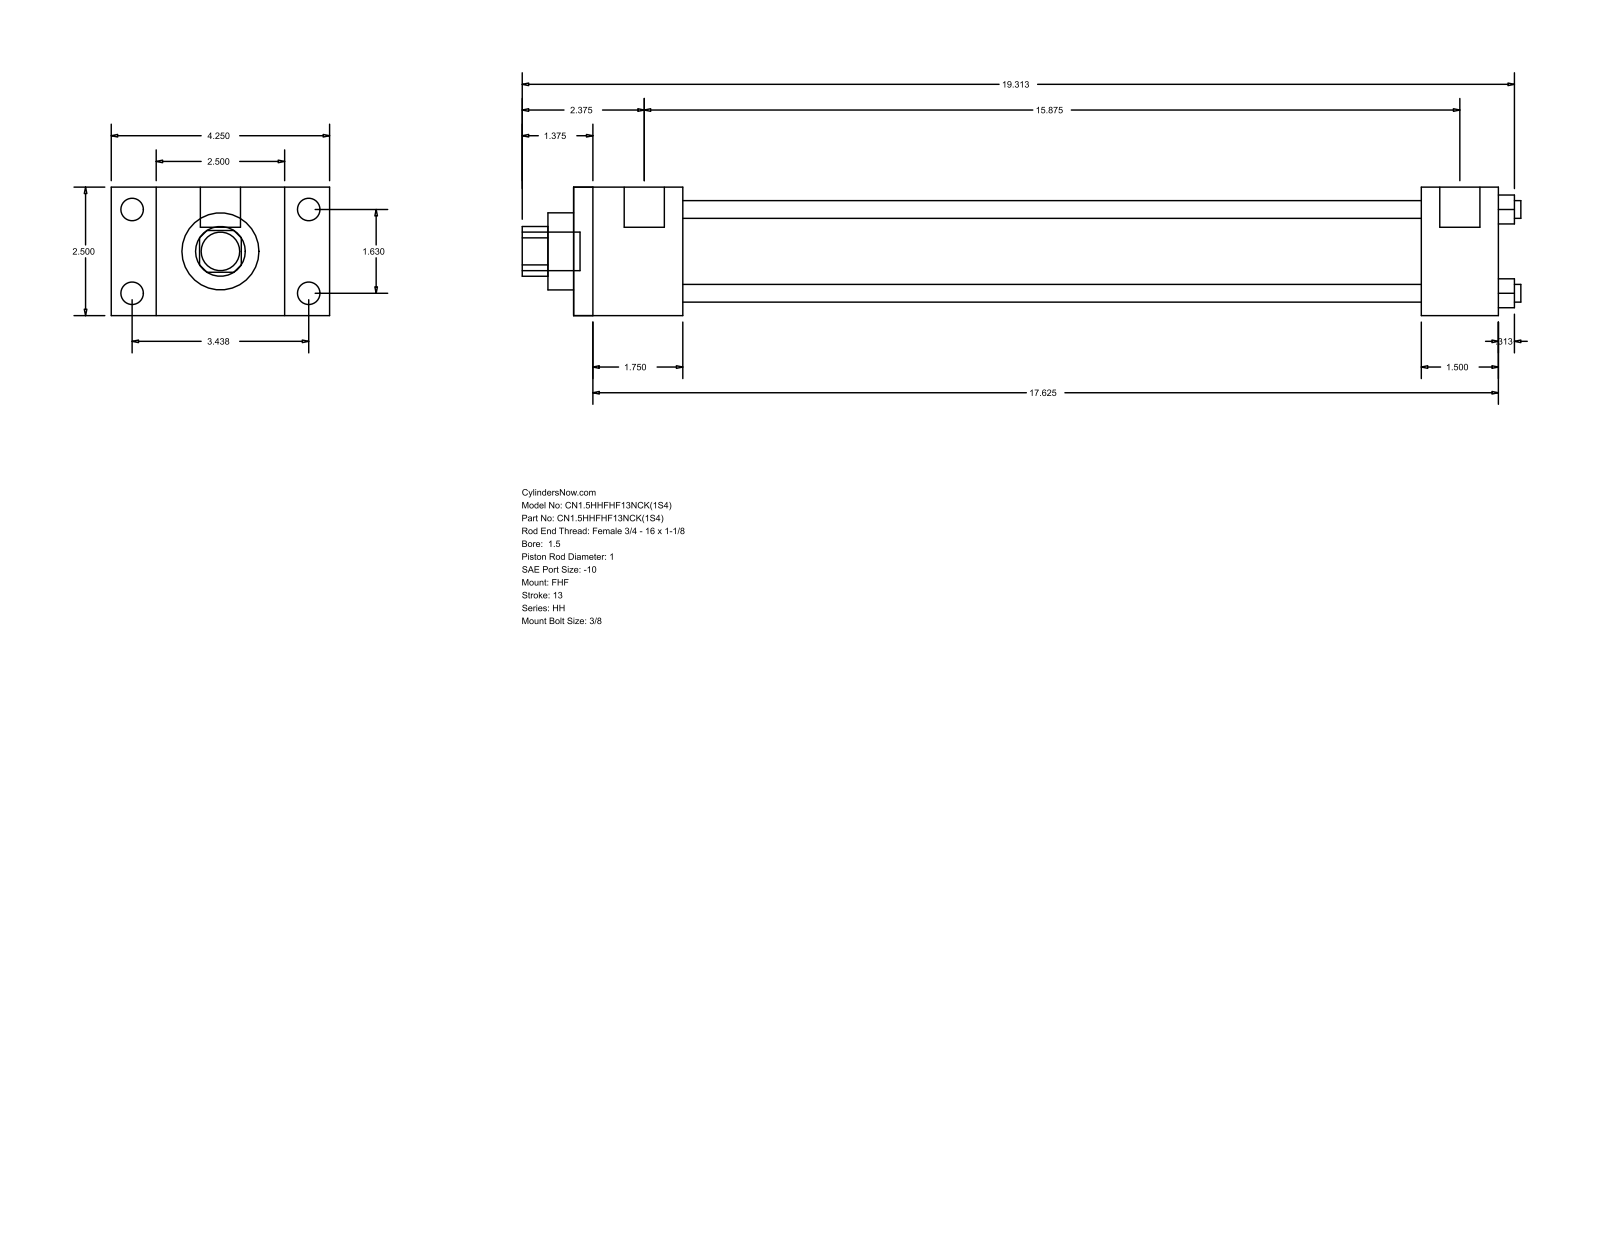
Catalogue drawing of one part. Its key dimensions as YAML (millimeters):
part_name: "HH_FHF__0150_1"
step_written_by: "GSSL Pune (CONFIG_CONTROL_DESIGN)"
units: millimeters
bodies: {solids: 0, faces: 88, planar: 60, cylindrical: 28, other: 0}
overall_size: [493.71, 107.95, 63.5]
round_holes:
  - {diameter: 8.76, count: 4}
  - {diameter: 25.4, count: 1}
  - {diameter: 38.1, count: 1}
  - {diameter: 44.45, count: 1}
round_bosses_or_shafts:
  - {diameter: 11.13, count: 4}
  - {diameter: 5.56, count: 4}
  - {diameter: 19.84, count: 2}
  - {diameter: 19.05, count: 1}
partial_cylinders:
  - {radius: 12.29, count: 1}
face_to_face_distances: [63.5, 22.23, 85.73, 53.98, 107.96, 457.2, 403.22, 419.1, 365.12, 38.1]
hole_center_spacings: [29.27, 41.4, 58.55]
